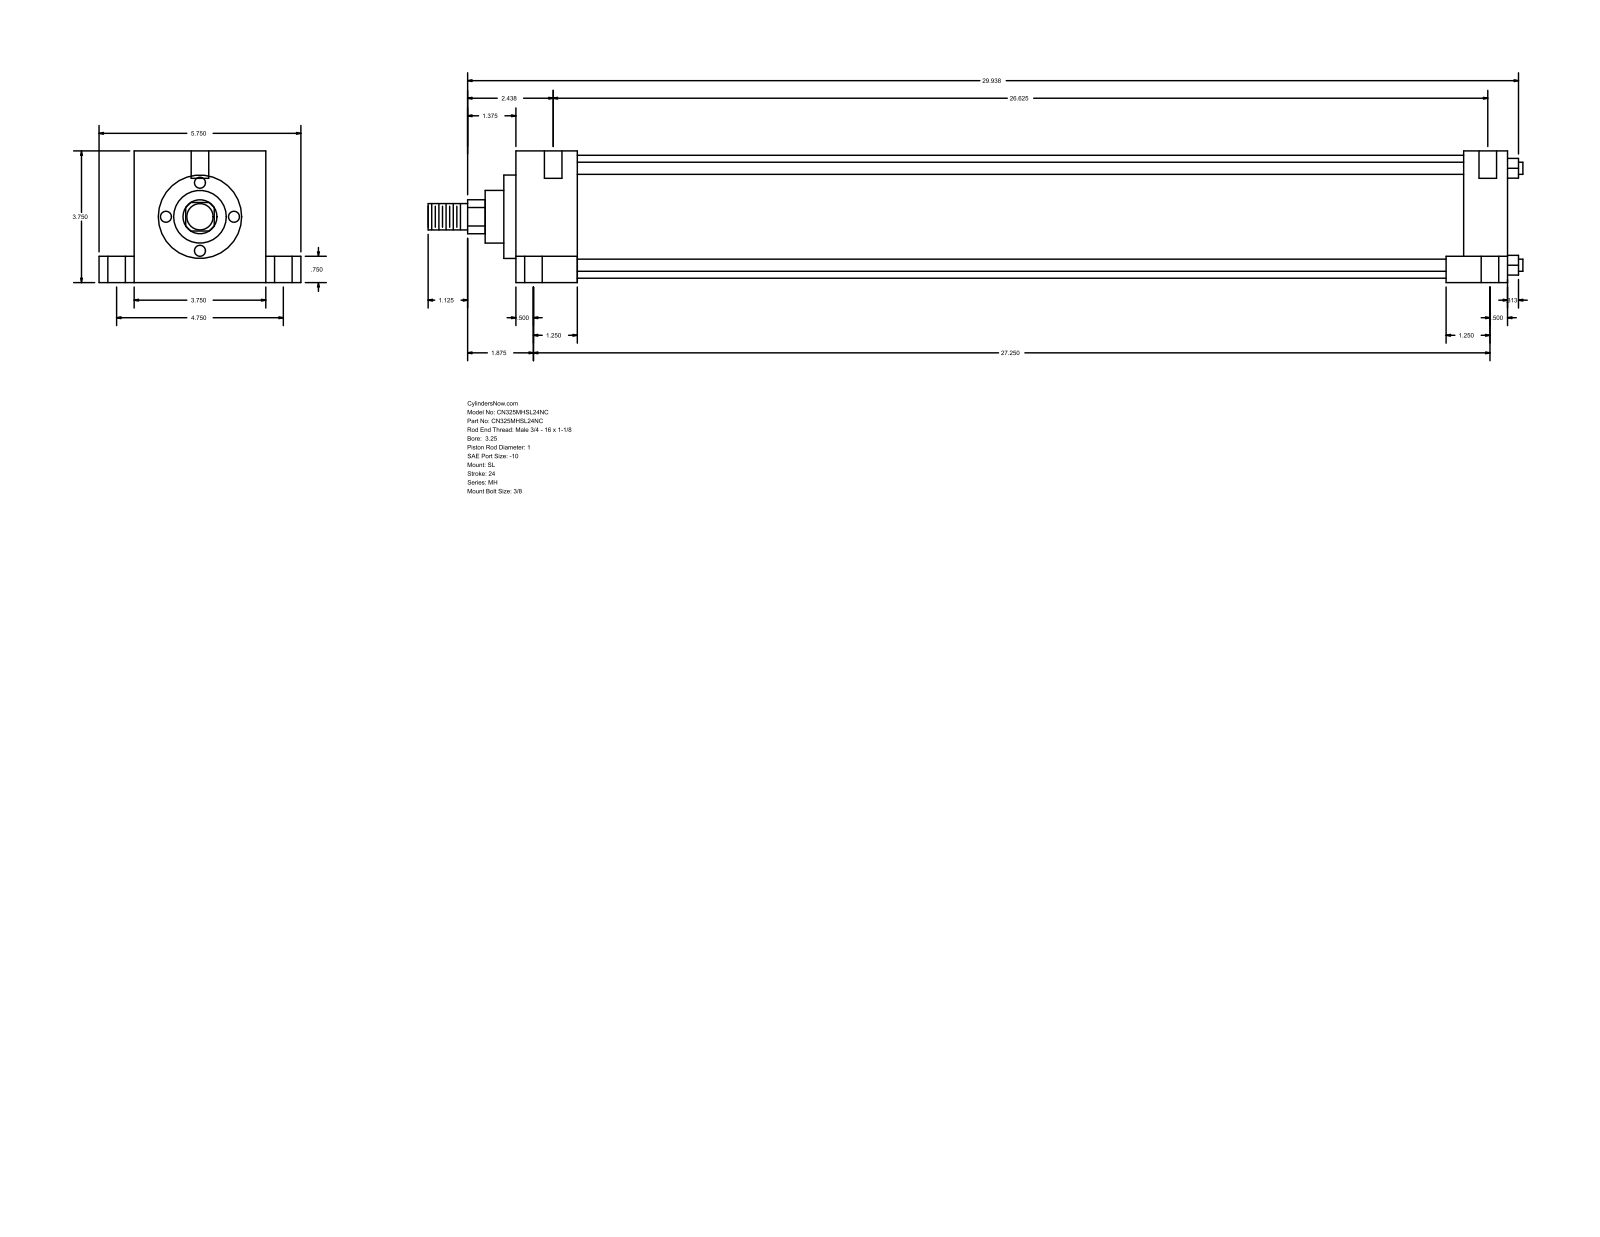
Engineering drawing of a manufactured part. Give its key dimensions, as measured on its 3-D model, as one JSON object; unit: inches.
{"part_name": "MH_SL__0325_1", "step_written_by": "GSSL Pune (CONFIG_CONTROL_DESIGN)", "units": "inches", "bodies": {"solids": 0, "faces": 110, "planar": 77, "cylindrical": 33, "other": 0}, "overall_size": [31.187, 5.75, 3.75], "round_holes": [[0.5, 6], [0.219, 4], [0.75, 4]], "round_bosses_or_shafts": [[0.345, 4], [3.5, 1], [2.375, 1], [1.5, 1], [1, 1], [0.75, 1]], "partial_cylinders_radius": [[0.484, 1]], "face_to_face_distances": [3.75, 28.25, 1.75, 26.5, 1, 4.75, 0.75, 3, 27, 25.25], "hole_center_spacings": [2.376, 2.378, 2.427, 2.441, 4.75, 26.793, 26.855, 26.875]}
